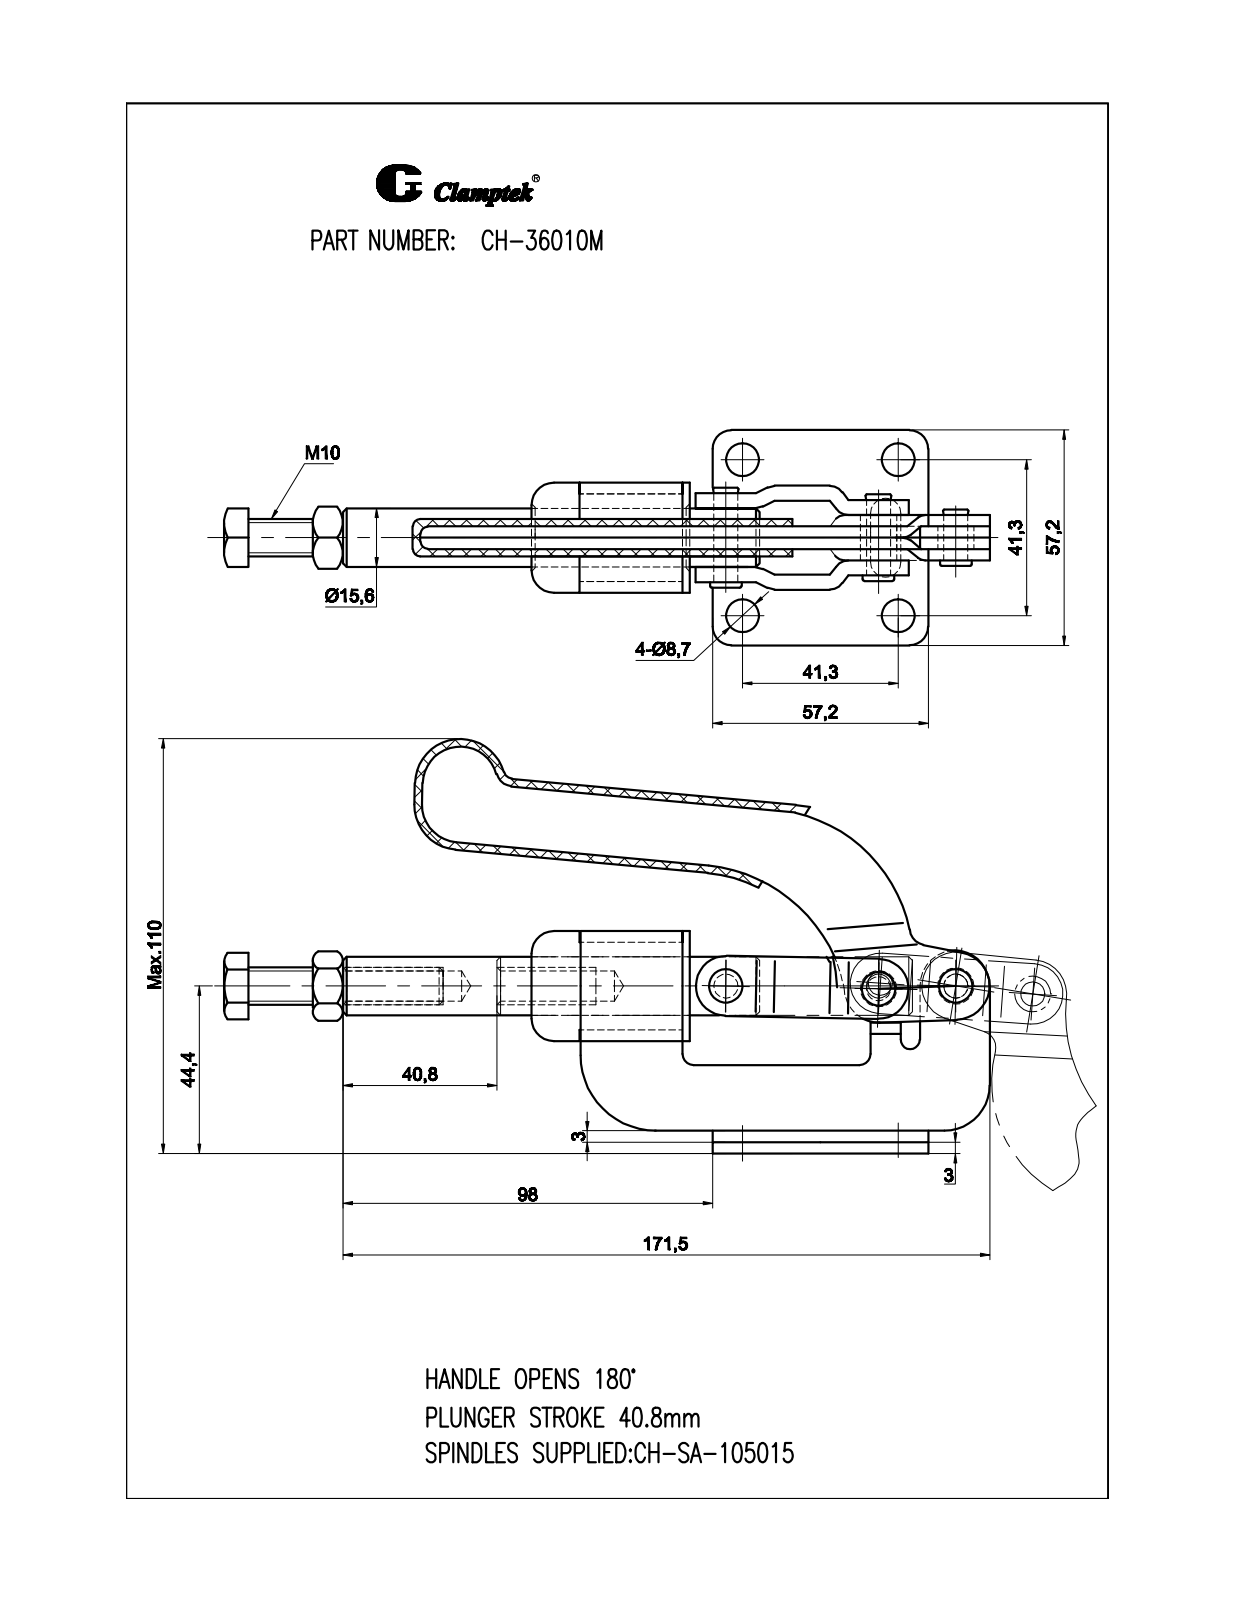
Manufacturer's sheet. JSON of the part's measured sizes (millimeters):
{"part_name": "CH-36010M-05 LEAD SET; CH-36010M-02 CREST STALK; CH-36010M-03 HANDLE; CH-36010M-07 (+8 more)", "step_written_by": "SolidWorks 2010 (CONFIG_CONTROL_DESIGN)", "units": "millimeters", "bodies": {"solids": 15, "faces": 796, "planar": 271, "cylindrical": 257, "other": 268}, "overall_size": [199.47, 116.27, 57.2], "volume_mm3": 114435, "surface_area_mm2": 69214, "round_holes": [[8.7, 4], [5.8, 3], [6.4, 3], [9.5, 2], [2.32, 1], [8.5, 1], [15.6, 1], [23.2, 1]], "round_bosses_or_shafts": [[29.2, 1], [10, 1], [6.46, 1], [1.96, 1]], "partial_cylinders_radius": [[3, 13], [4, 8], [1, 6], [5, 4], [4, 2], [8, 2], [11.5, 2], [2.55, 1]], "face_to_face_distances": [3, 6, 1.5, 9, 4.5, 7.5, 2, 10.5, 4, 16], "hole_center_spacings": [41.3, 58.41, 20.49, 27.77, 41.51, 47.36, 61.98, 65.54]}
